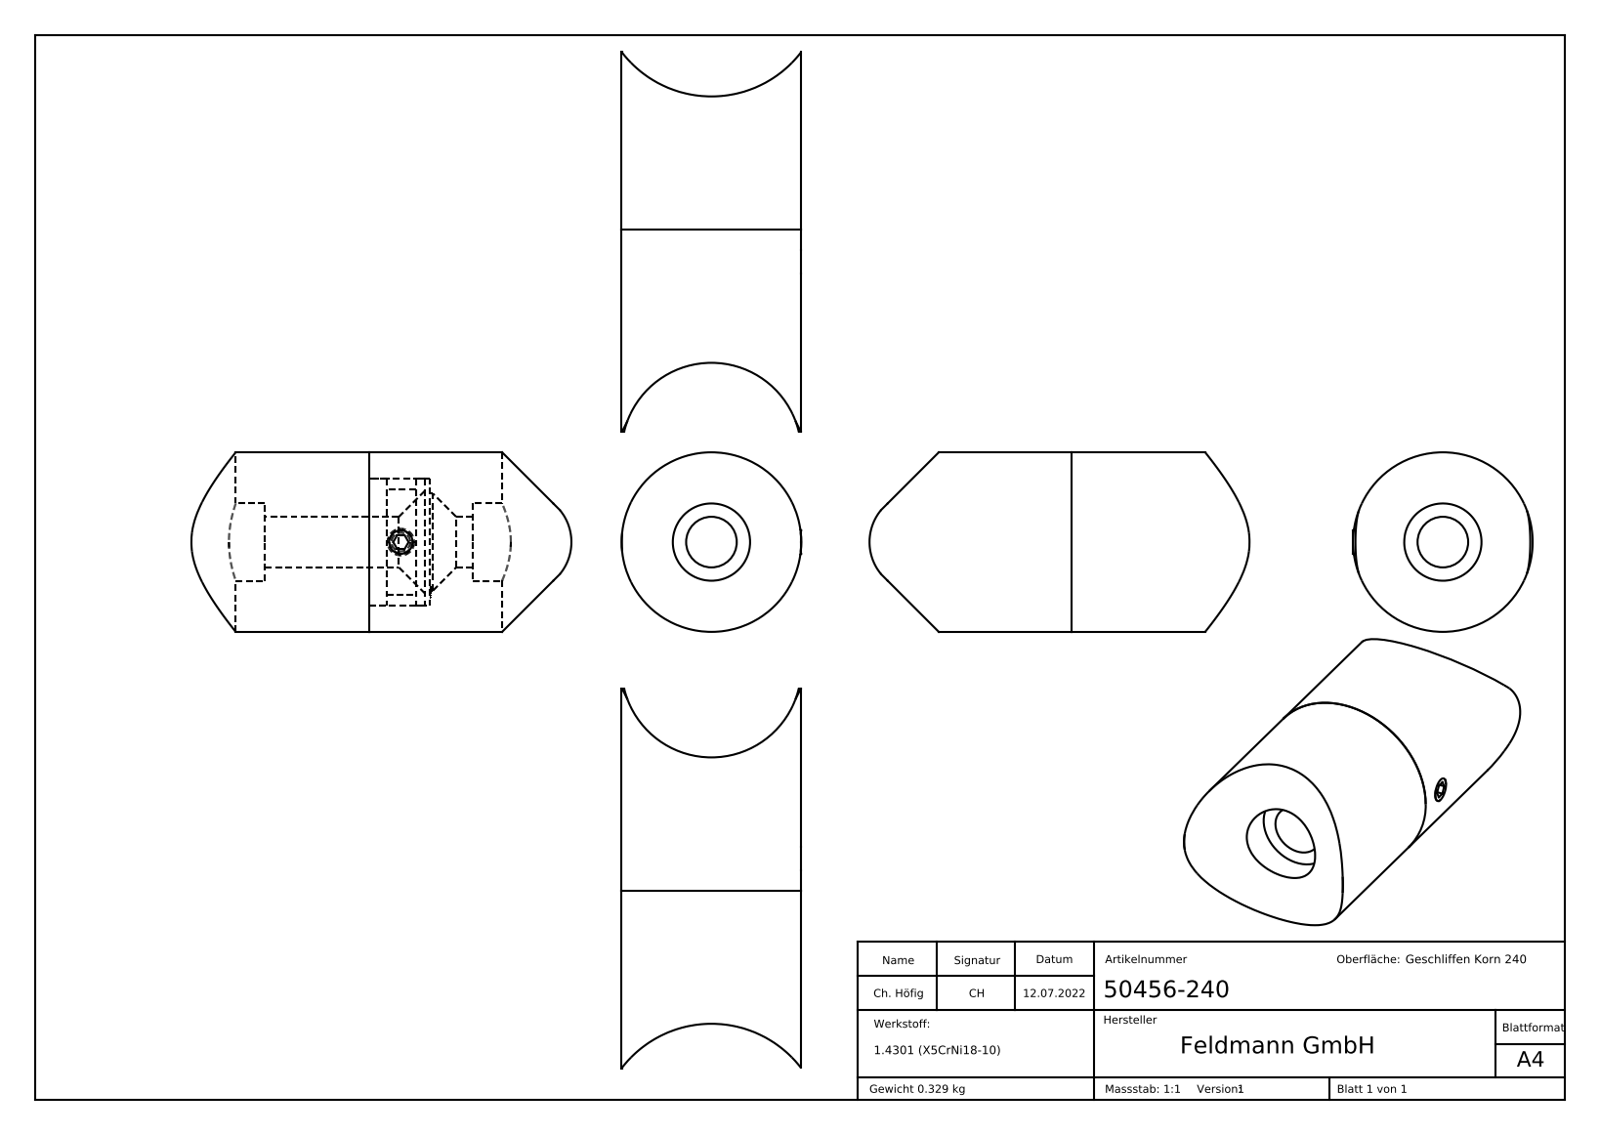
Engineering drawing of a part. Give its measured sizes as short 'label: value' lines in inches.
name: 50456-240 Teil2_50456-240 Teil2; 50456-240 DIN913 M5x6_DIN913 M5x6; 50456-240; 50456-240 Teil1_50456-240 Teil1
written by: SolidWorks 2018 (CONFIG_CONTROL_DESIGN)
unit: in
bodies: 3 solids, 267 faces (147 planar, 19 cylindrical, 101 other)
size: 2.808 × 1.327 × 1.327
volume: 2.543 in³; area: 21.01 in²
holes: 1× ⌀0.165, 1× ⌀0.374, 1× ⌀0.571, 1× ⌀0.719, 1× ⌀0.945
bosses: 1× ⌀1.327, 1× ⌀0.935, 1× ⌀0.778, 1× ⌀0.197
rounds: 1× R0.371, 1× R0.591, 1× R0.663, 1× R0.835
face distances: 0.453, 0.768, 0.039, 0.413, 0.106, 0.067, 0.346, 0.323, 0.283, 0.217
